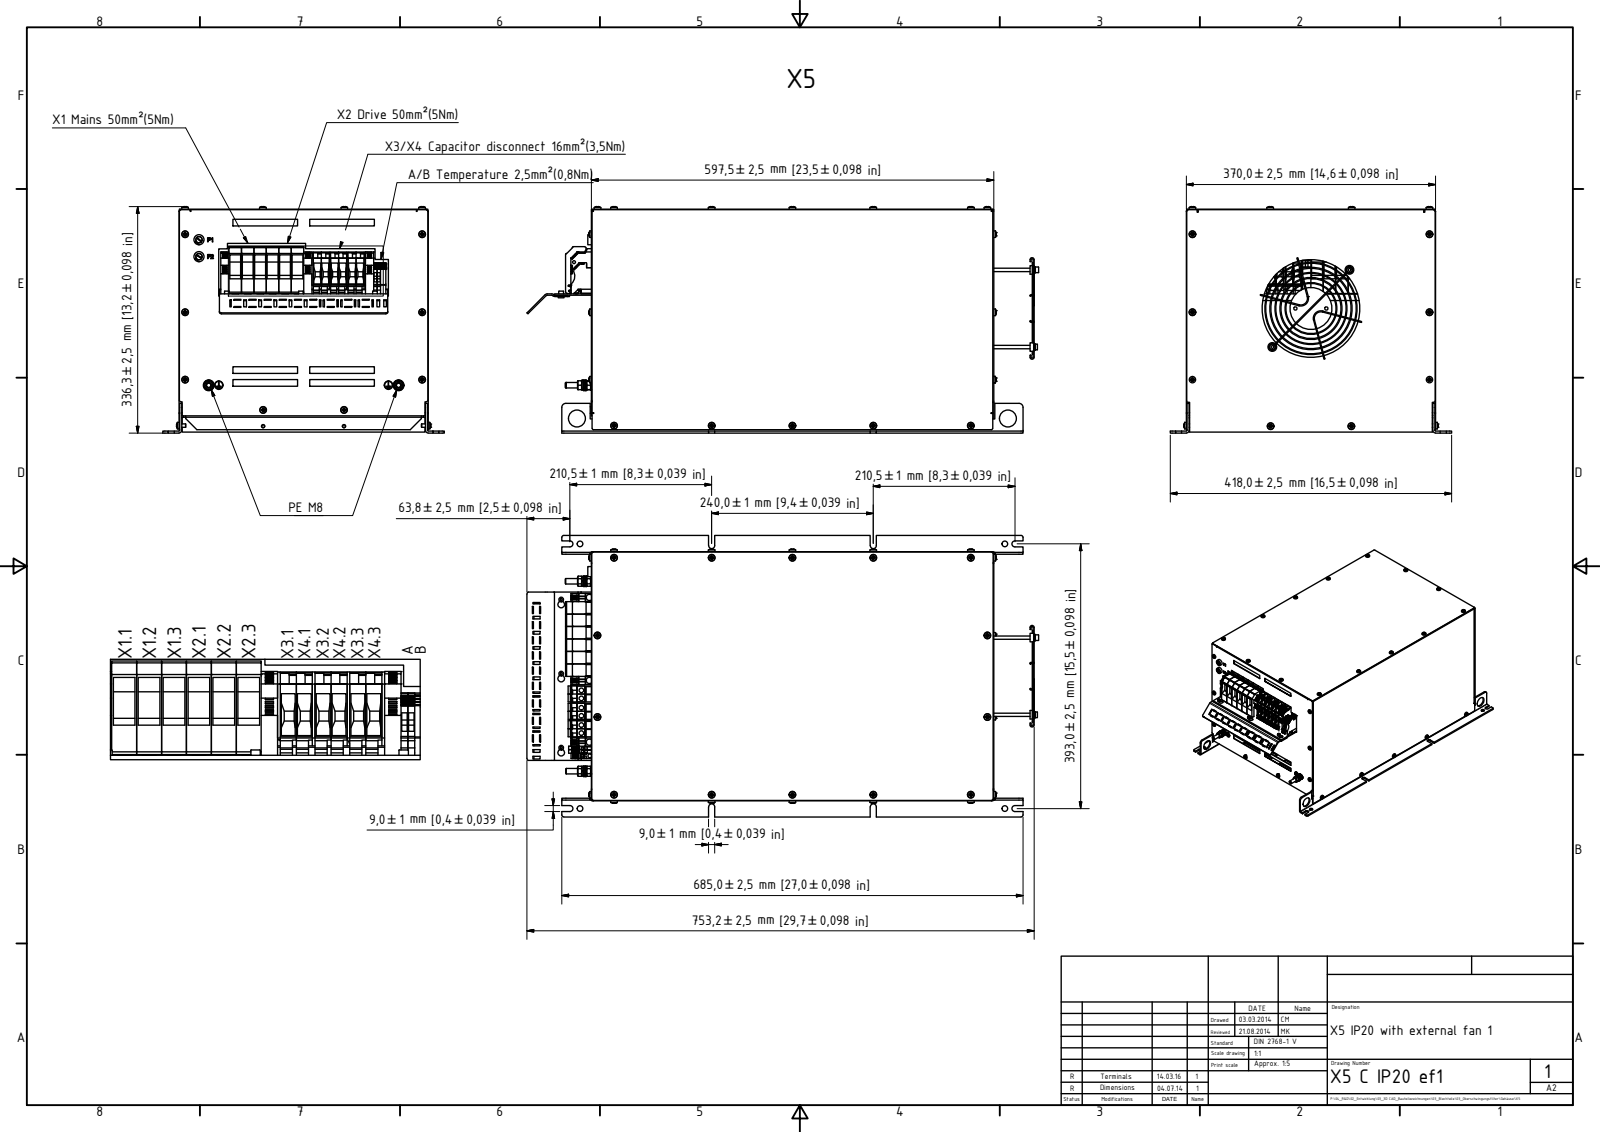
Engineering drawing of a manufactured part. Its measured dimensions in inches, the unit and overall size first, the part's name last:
Units: inches
Overall size (bounding box): 29.861 × 16.457 × 13.241
Round holes (diameter × count): ⌀0.163 ×29, ⌀0.256 ×27, ⌀0.268 ×14, ⌀0.236 ×11, ⌀0.276 ×11, ⌀0.354 ×8, ⌀0.128 ×7, ⌀0.335 ×6, ⌀0.157 ×5, ⌀0.323 ×4, ⌀0.156 ×3, ⌀0.37 ×3
Round bosses / shafts (diameter × count): ⌀0.197 ×31, ⌀0.181 ×29, ⌀0.055 ×8, ⌀0.335 ×5, ⌀0.63 ×4, ⌀0.449 ×4, ⌀0.362 ×4, ⌀0.276 ×3
Partial cylindrical surfaces — rounded edges, fillets, slot ends (radius × count): R0.009 ×112, R0.02 ×76, R0.039 ×70, R0.006 ×56, R0.079 ×53, R0.004 ×41, R0.004 ×37, R0.008 ×29
Main face-to-face distances: 0.039, 14.528, 0.118, 14.488, 14.567, 12.165, 12.126, 12.047, 12.008, 0.059
Hole centre spacings: 0.827, 13.858, 4.724, 1.432, 5.709, 10.433, 15.157, 1.063
Volume: 152.3 in³ · Surface area: 4 292 in²
Bodies: 111 solids, 8073 faces (4720 planar, 2040 cylindrical, 1313 other)
Part name (STEP PRODUCT): 10100398 Deckel X5_X6; 10100399 Seitenwand X5; 10100396 Anschlussblech X5; 10100397 Lüfterblech X5 (+8 more)
STEP written by: Autodesk Inventor 2015 (AUTOMOTIVE_DESIGN)
